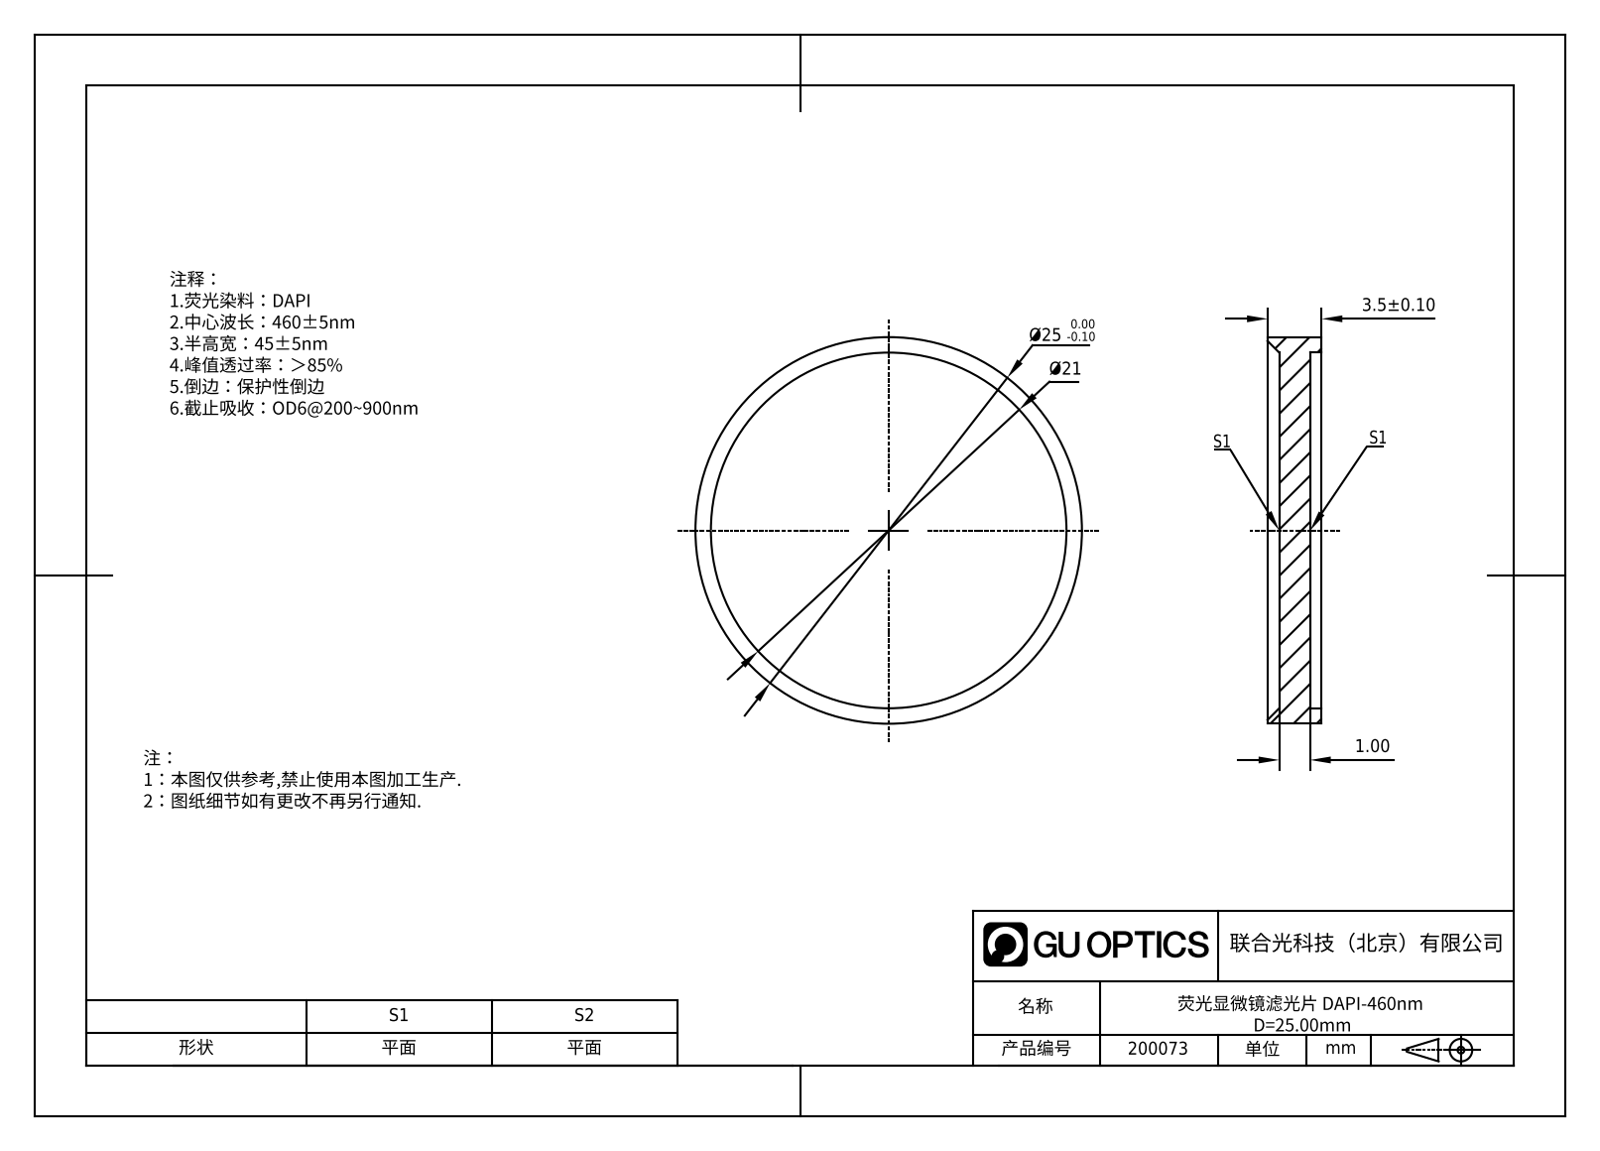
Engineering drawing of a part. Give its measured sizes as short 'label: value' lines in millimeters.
name: GNIF-045-460-D25
written by: SolidWorks 2022 (AUTOMOTIVE_DESIGN)
unit: mm
bodies: 1 solid, 10 faces (4 planar, 4 cylindrical, 2 other)
size: 25 × 25 × 3.5
volume: 1 074 mm³; area: 1 334 mm²
holes: 1× ⌀23
bosses: 1× ⌀25
face distances: 2, 0.75, 2.75, 3.5
